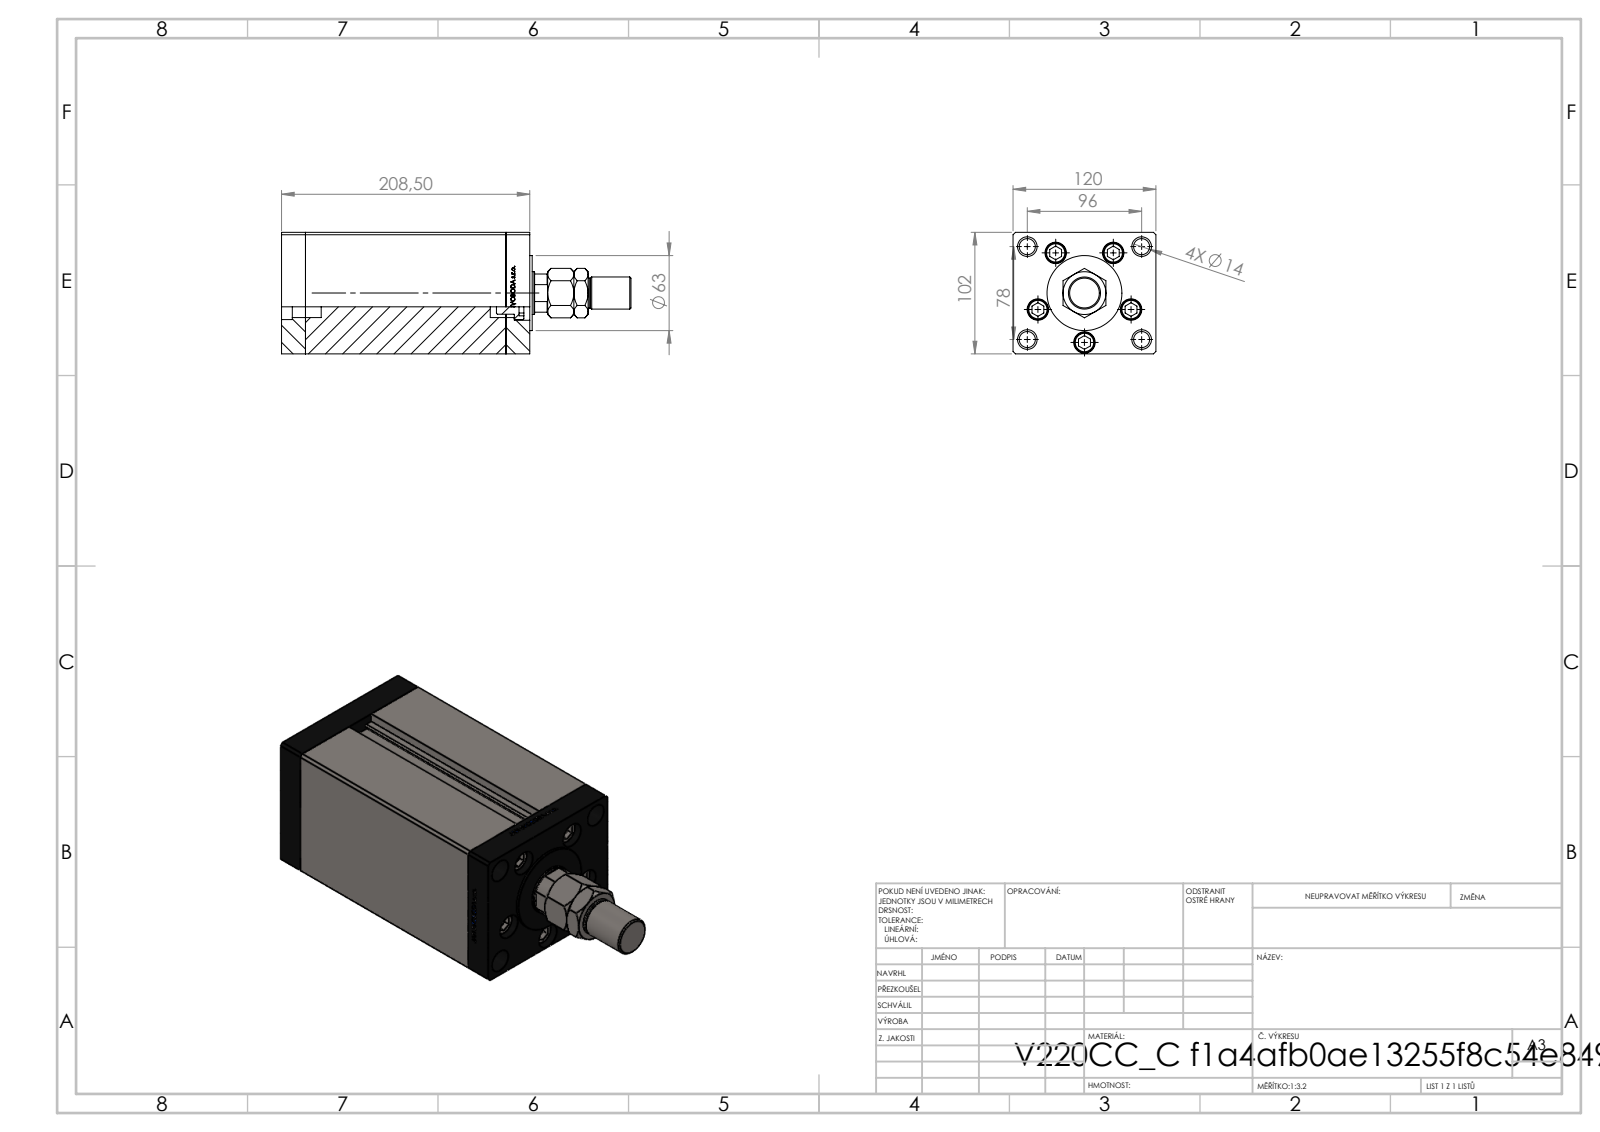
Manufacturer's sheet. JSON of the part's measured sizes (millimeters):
{"part_name": "V220C_C MIDDLE; V220C BACK_C; V220C FRONT; MTA (+2 more)", "step_written_by": "SolidWorks 2019 (CONFIG_CONTROL_DESIGN)", "units": "millimeters", "bodies": {"solids": 14, "faces": 1214, "planar": 557, "cylindrical": 165, "other": 492}, "overall_size": [293.5, 120, 102], "volume_mm3": 2199000, "surface_area_mm2": 307904, "round_holes": [[13.5, 9], [18, 5], [12, 4], [16.5, 4], [17, 1], [25.5, 1], [36, 1]], "round_bosses_or_shafts": [[8, 5], [17, 4], [63, 1], [27, 1], [25, 1]], "partial_cylinders_radius": [[0.93, 2], [17.5, 1]], "face_to_face_distances": [120, 102, 20, 168.5, 188.5, 34.25, 208.5, 174.25, 154.25, 14.25], "hole_center_spacings": [41.5, 61.85, 24.39, 26.69, 47.92, 48.07, 49.84, 53.57]}
